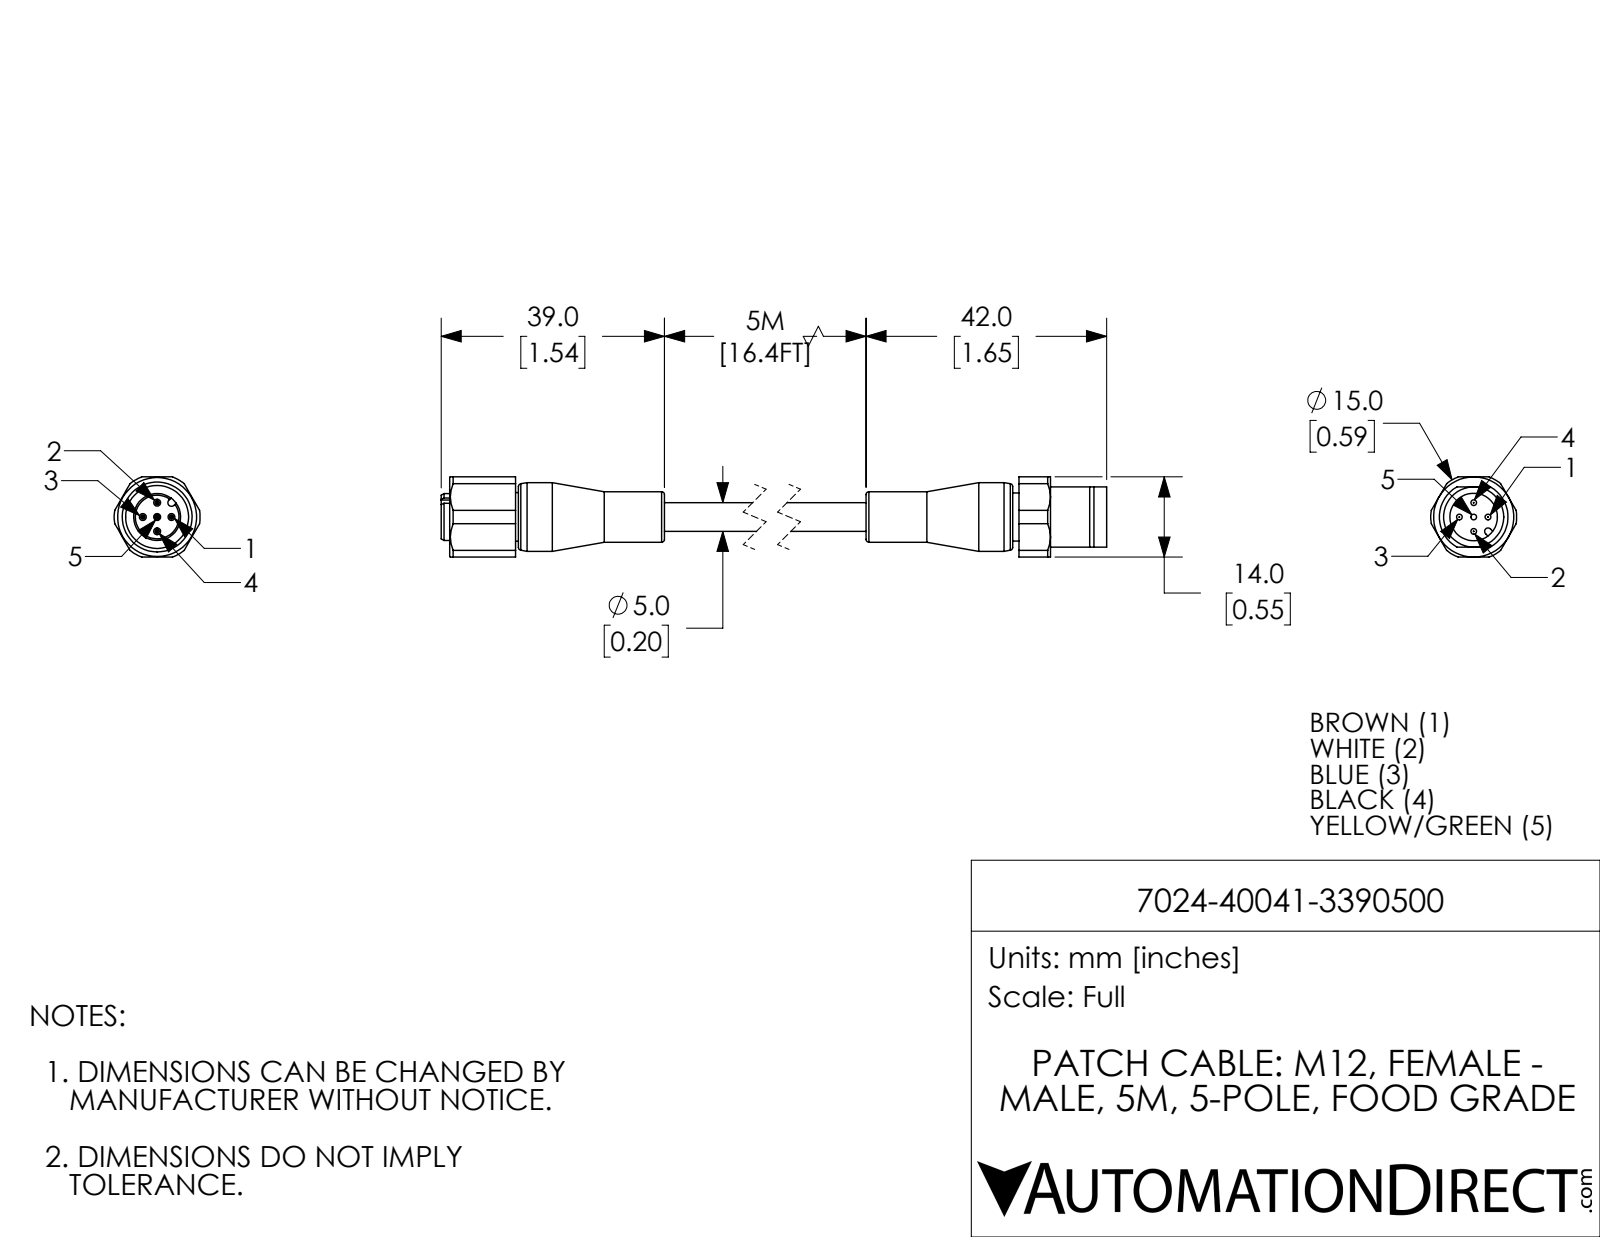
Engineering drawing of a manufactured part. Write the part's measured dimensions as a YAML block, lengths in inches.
part_name: "7024-40041-3390500_FEMALE; 7024-40041-3390500; 7024-40041-3390500_MALE"
step_written_by: "SolidWorks 2018 (AUTOMOTIVE_DESIGN)"
units: inches
bodies: {solids: 2, faces: 148, planar: 43, cylindrical: 62, other: 43}
overall_size: [5.165, 0.591, 0.551]
volume: 0.491
surface_area: 7.892
round_holes:
  - {diameter: 0.047, count: 5}
  - {diameter: 0.327, count: 1}
  - {diameter: 0.433, count: 1}
round_bosses_or_shafts:
  - {diameter: 0.039, count: 5}
  - {diameter: 0.472, count: 1}
  - {diameter: 0.413, count: 1}
  - {diameter: 0.346, count: 1}
  - {diameter: 0.335, count: 1}
  - {diameter: 0.331, count: 1}
  - {diameter: 0.323, count: 1}
  - {diameter: 0.197, count: 1}
partial_cylinders:
  - {radius: 0.024, count: 1}
  - {radius: 0.026, count: 1}
  - {radius: 0.295, count: 1}
face_to_face_distances: [0.551, 4.051, 0.069, 0.482, 4.461, 0.295, 0.217, 4.303, 0.252, 4.268]
hole_center_spacings: [0.098, 0.139, 0.197]
